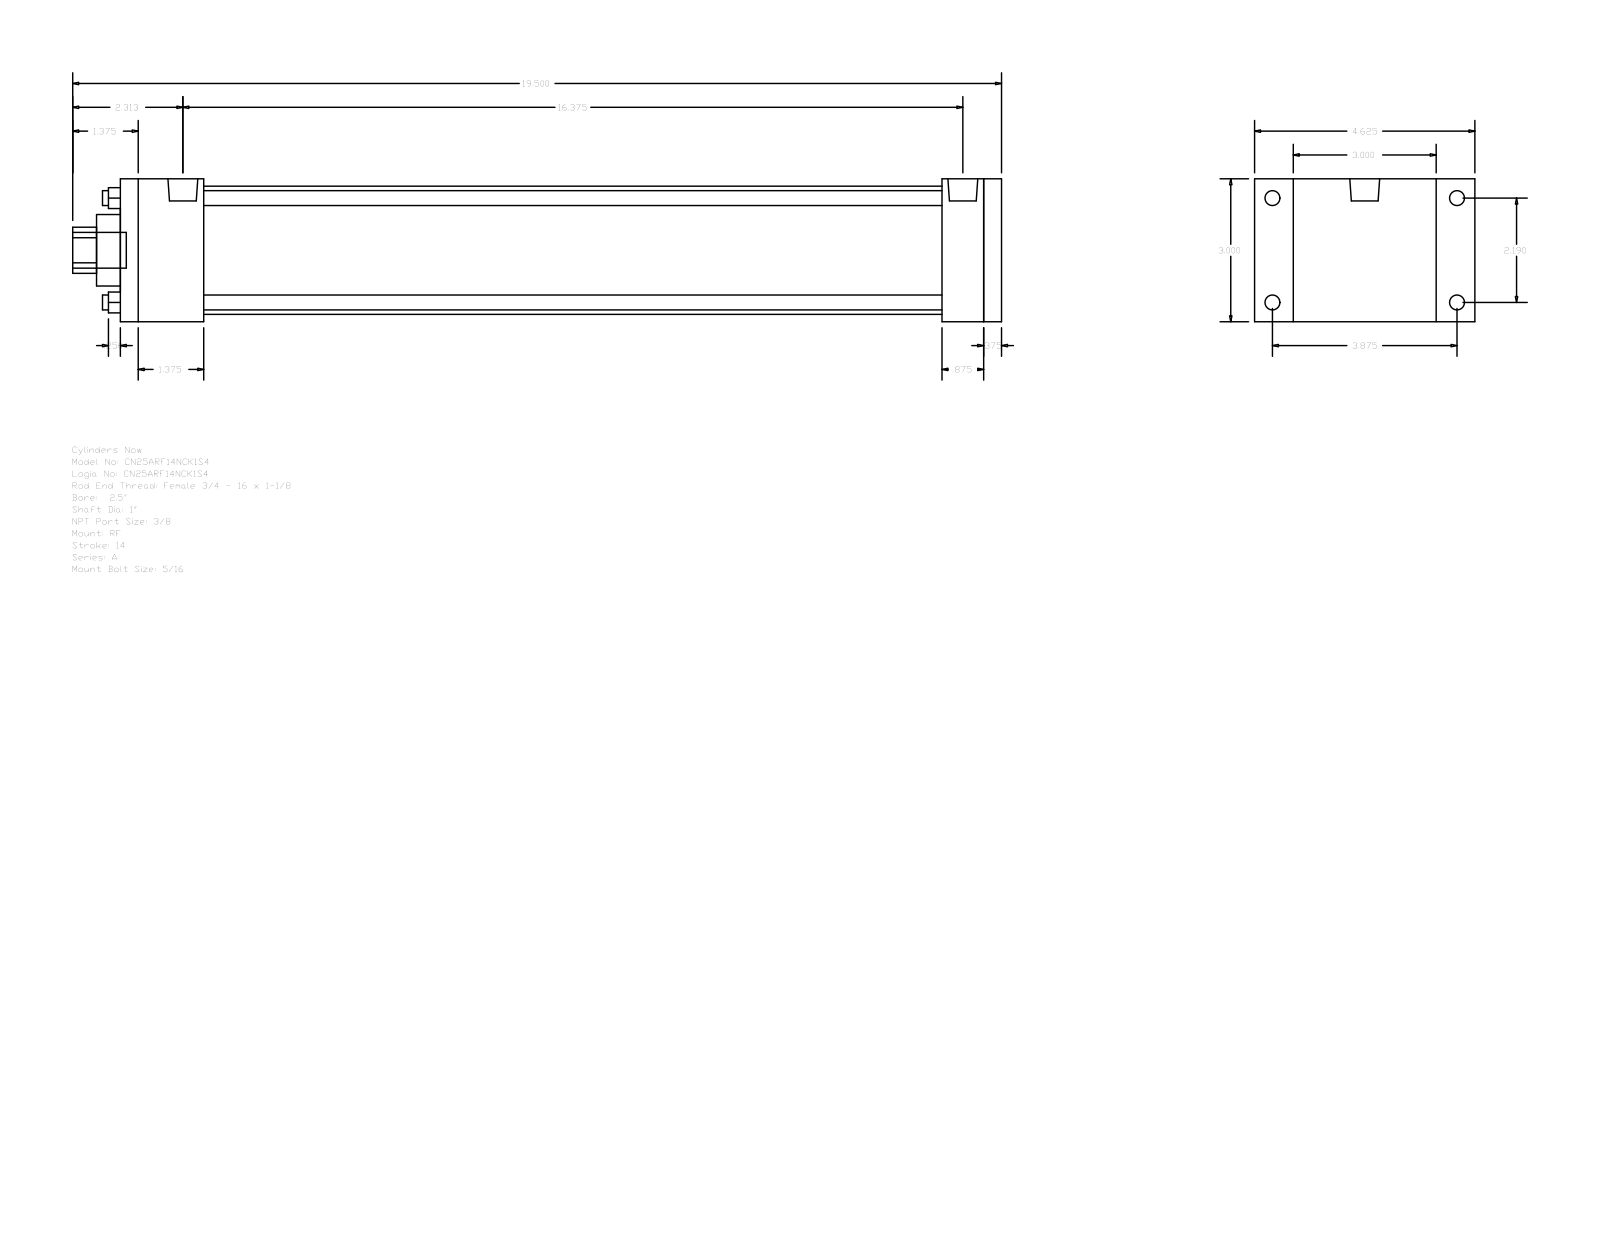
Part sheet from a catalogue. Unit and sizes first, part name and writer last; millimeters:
Units: millimetres
Overall size (bounding box): 495.3 × 117.47 × 76.2
Round holes (diameter × count): ⌀7.94 ×4, ⌀25.4 ×1, ⌀38.1 ×1, ⌀68.33 ×1
Round bosses / shafts (diameter × count): ⌀7.94 ×4, ⌀5.56 ×4, ⌀15.93 ×2, ⌀19.05 ×1
Partial cylindrical surfaces — rounded edges, fillets, slot ends (radius × count): R12.29 ×1
Main face-to-face distances: 76.2, 469.9, 9.53, 460.37, 44.45, 438.15, 393.7, 415.92, 425.45, 22.22
Hole centre spacings: 39.33, 55.62, 78.66
Bodies: 0 solids, 92 faces (64 planar, 28 cylindrical, 0 other)
Part name (STEP PRODUCT): A_RF__0250_1
STEP written by: GSSL Pune (CONFIG_CONTROL_DESIGN)
